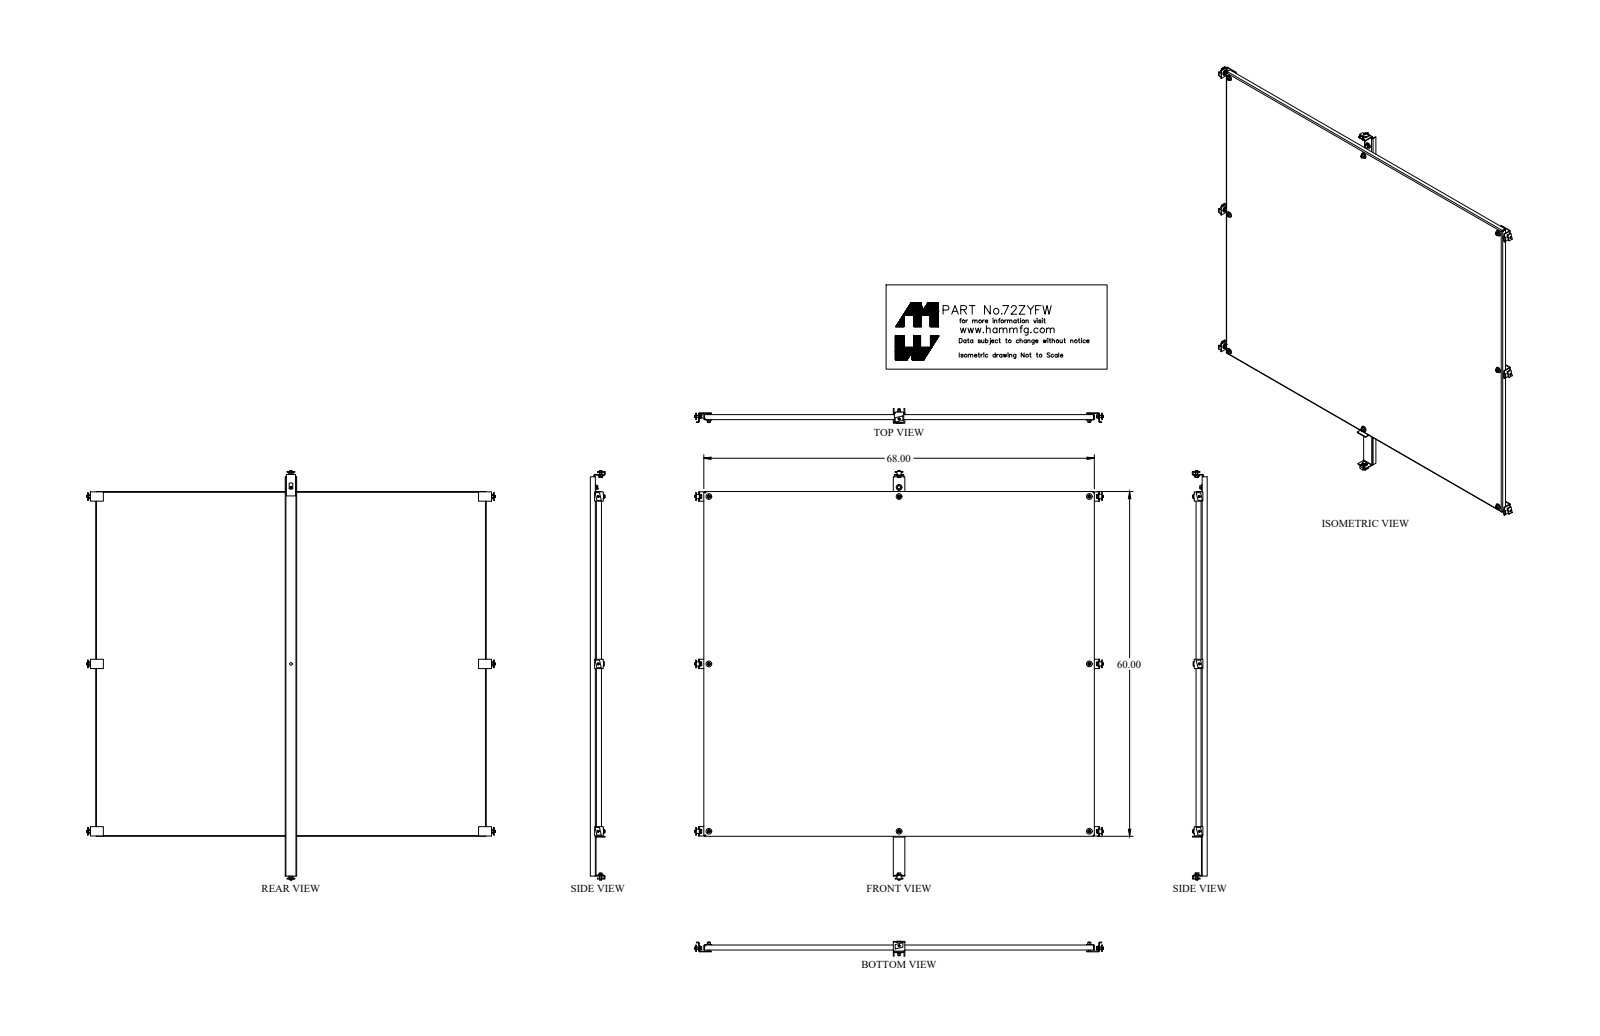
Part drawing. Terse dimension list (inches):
name: 72ZYFW_Default
written by: SolidWorks 2018 (CONFIG_CONTROL_DESIGN)
unit: in
bodies: 1 solid, 70 faces (38 planar, 24 cylindrical, 8 other)
size: 68 × 60 × 0.875
volume: 532 in³; area: 8 546 in²
holes: 8× ⌀0.563
rounds: 4× R0.06, 4× R0.185
face distances: 0.125, 59.875, 0.125, 67.875, 59.75, 60, 67.75, 68, 0.875, 0.75
hole spacings: 29.125, 33.125, 44.108, 67.01, 72.37, 58.25, 66.25, 88.217
